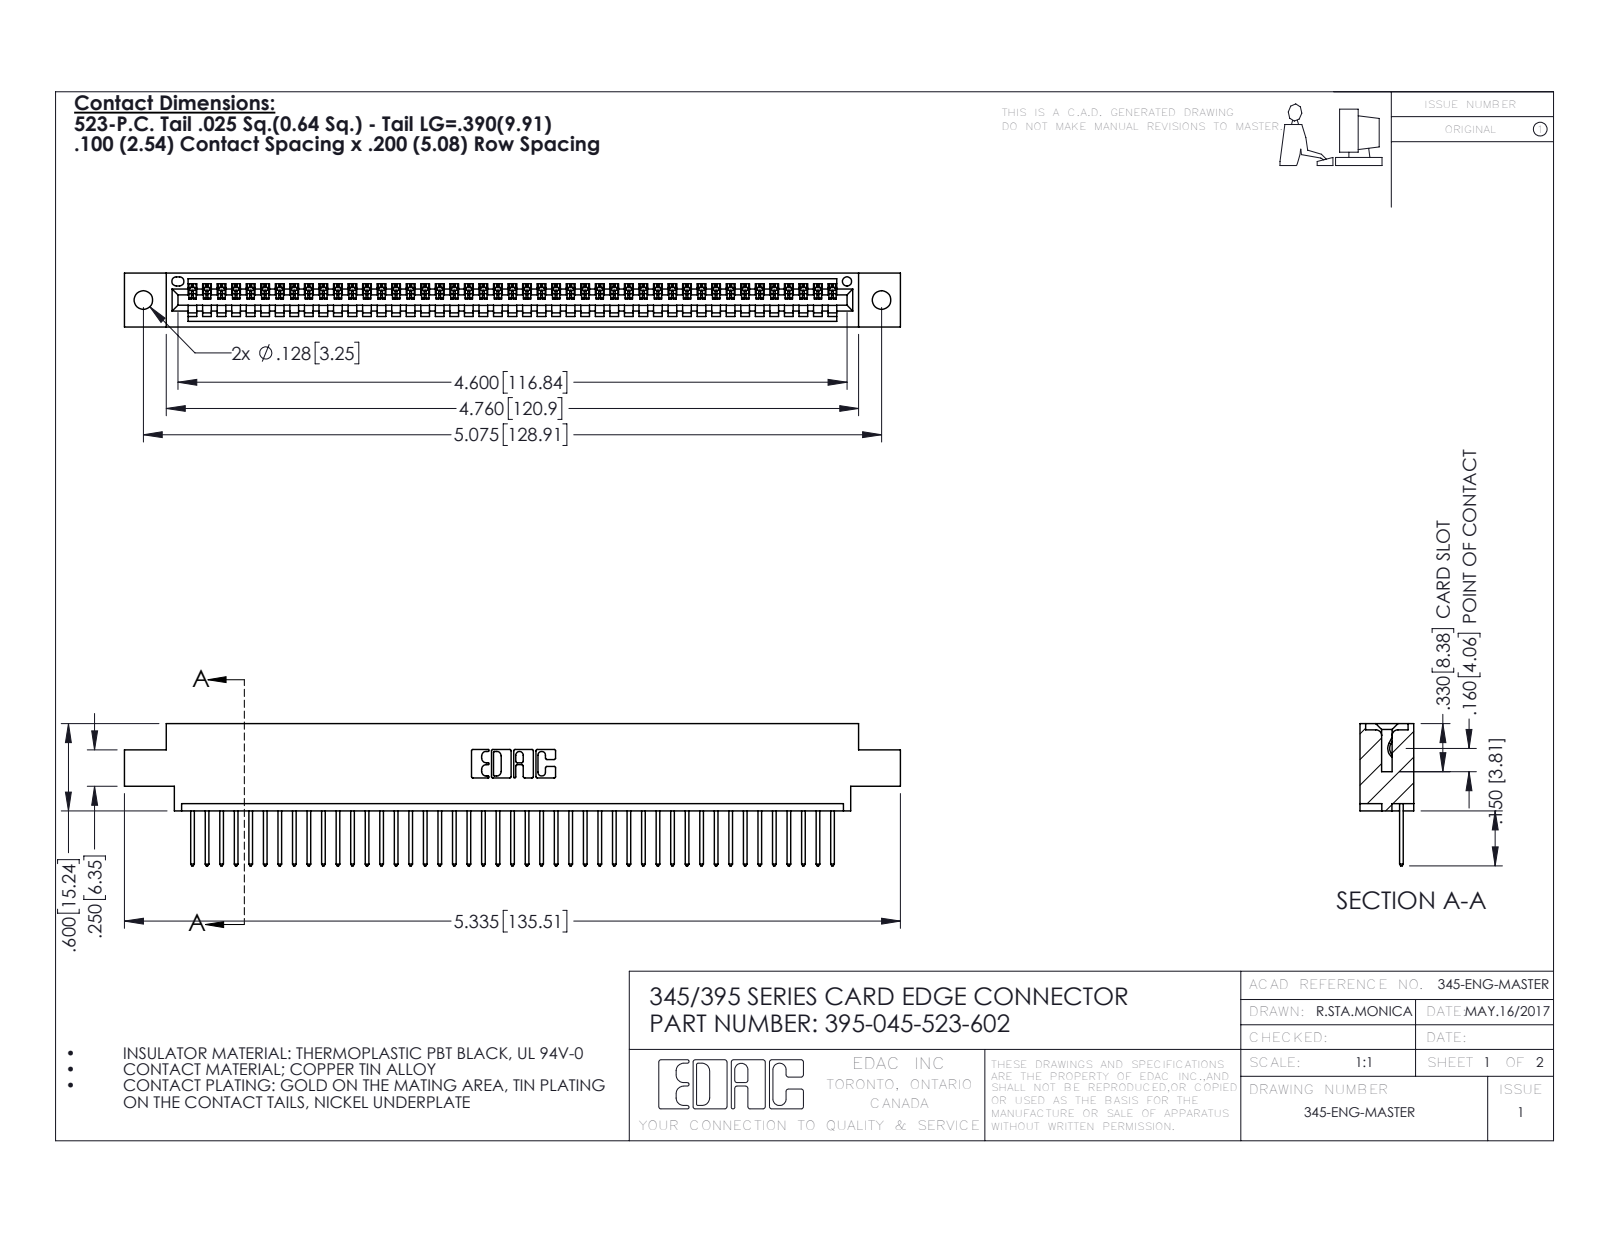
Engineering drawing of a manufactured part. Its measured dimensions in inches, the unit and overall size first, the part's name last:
Units: inches
Overall size (bounding box): 5.335 × 0.977 × 0.37
Round holes (diameter × count): ⌀0.128 ×2, ⌀0.064 ×1
Partial cylindrical surfaces — rounded edges, fillets, slot ends (radius × count): R0.006 ×90, R0.01 ×90, R0.01 ×22, R0.007 ×6, R0.031 ×6, R0.026 ×3, R0.031 ×2, R0.04 ×2
Main face-to-face distances: 0.298, 0.072, 0.37, 0.2, 0.098, 0.272, 0.025, 0.225, 0.175, 0.149
Hole centre spacings: 0.27, 4.839, 5.075
Volume: 0.777 in³ · Surface area: 26.13 in²
Bodies: 46 solids, 2740 faces (1884 planar, 856 cylindrical, 0 other)
Part name (STEP PRODUCT): 345-292-001_345-293-123; 345 Part_0.170 Offset - 0.128 Dia; 395-045-523-602
STEP written by: SolidWorks 2016 (CONFIG_CONTROL_DESIGN)
